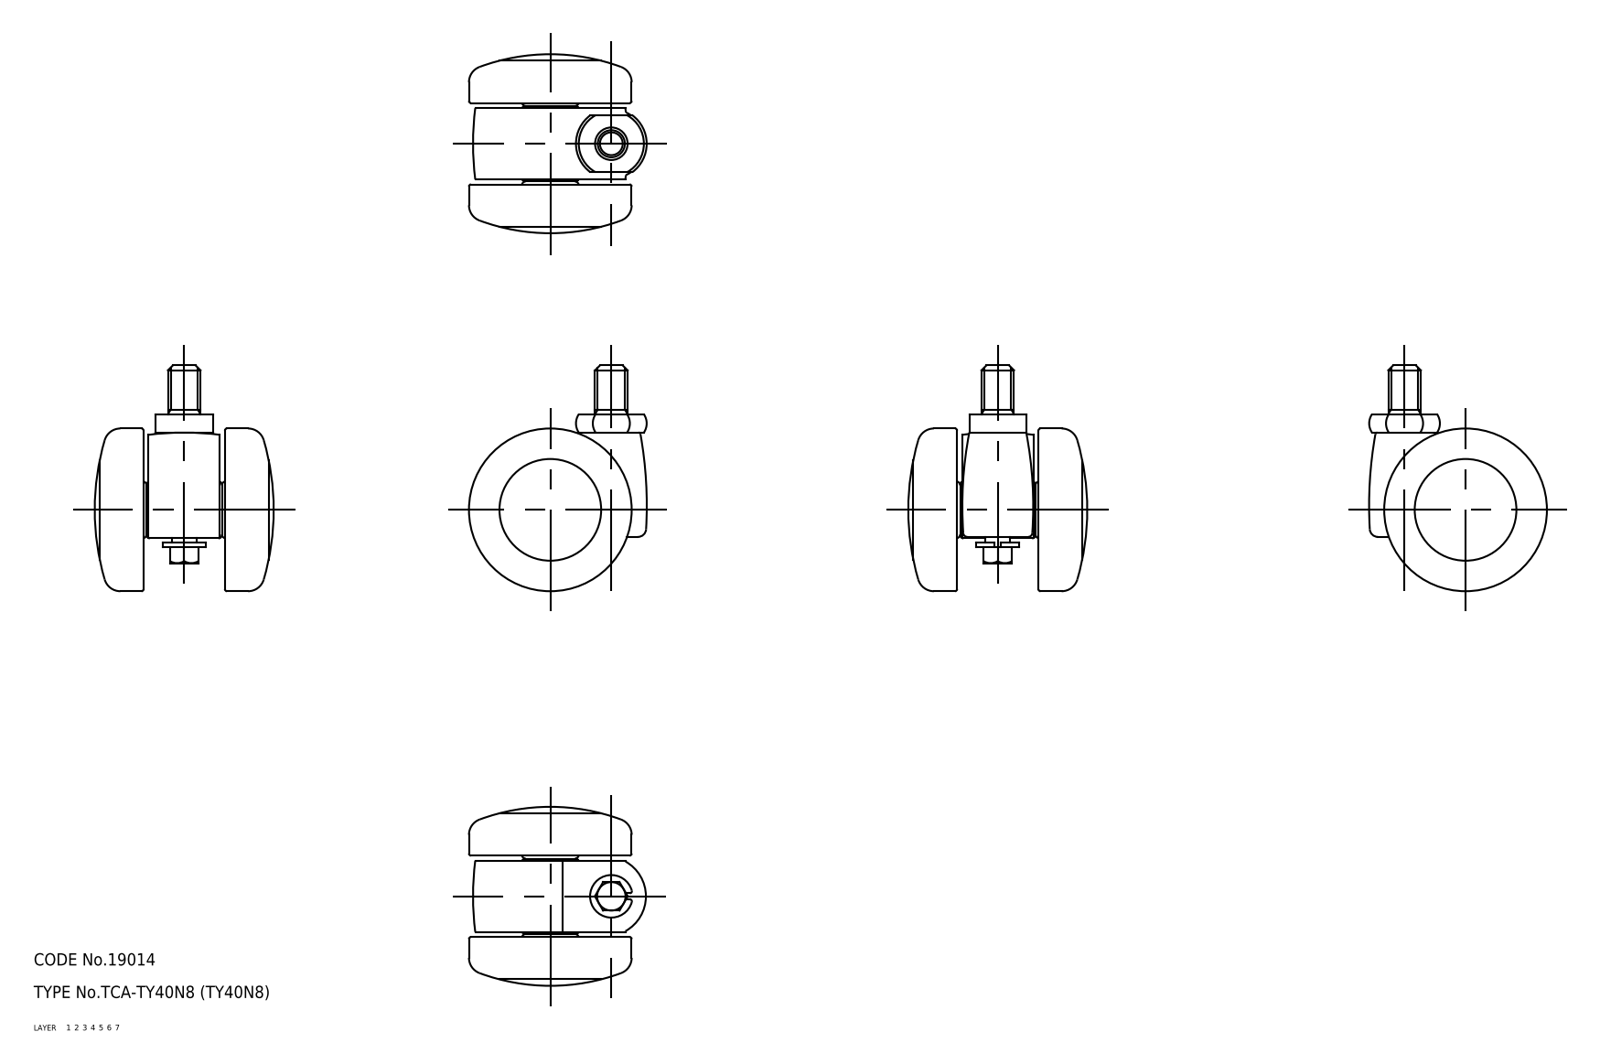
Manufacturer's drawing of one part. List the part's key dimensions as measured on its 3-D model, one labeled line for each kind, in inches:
Part name (STEP PRODUCT): wheel; main shaft; TY40N8_10554_36
STEP written by: CADfix (AUTOMOTIVE_DESIGN)
Units: inches
Bodies: 4 solids, 117 faces (0 planar, 0 cylindrical, 117 other)
Overall size (bounding box): 2.185 × 1.732 × 1.721
Volume: 2.353 in³ · Surface area: 26.97 in²
